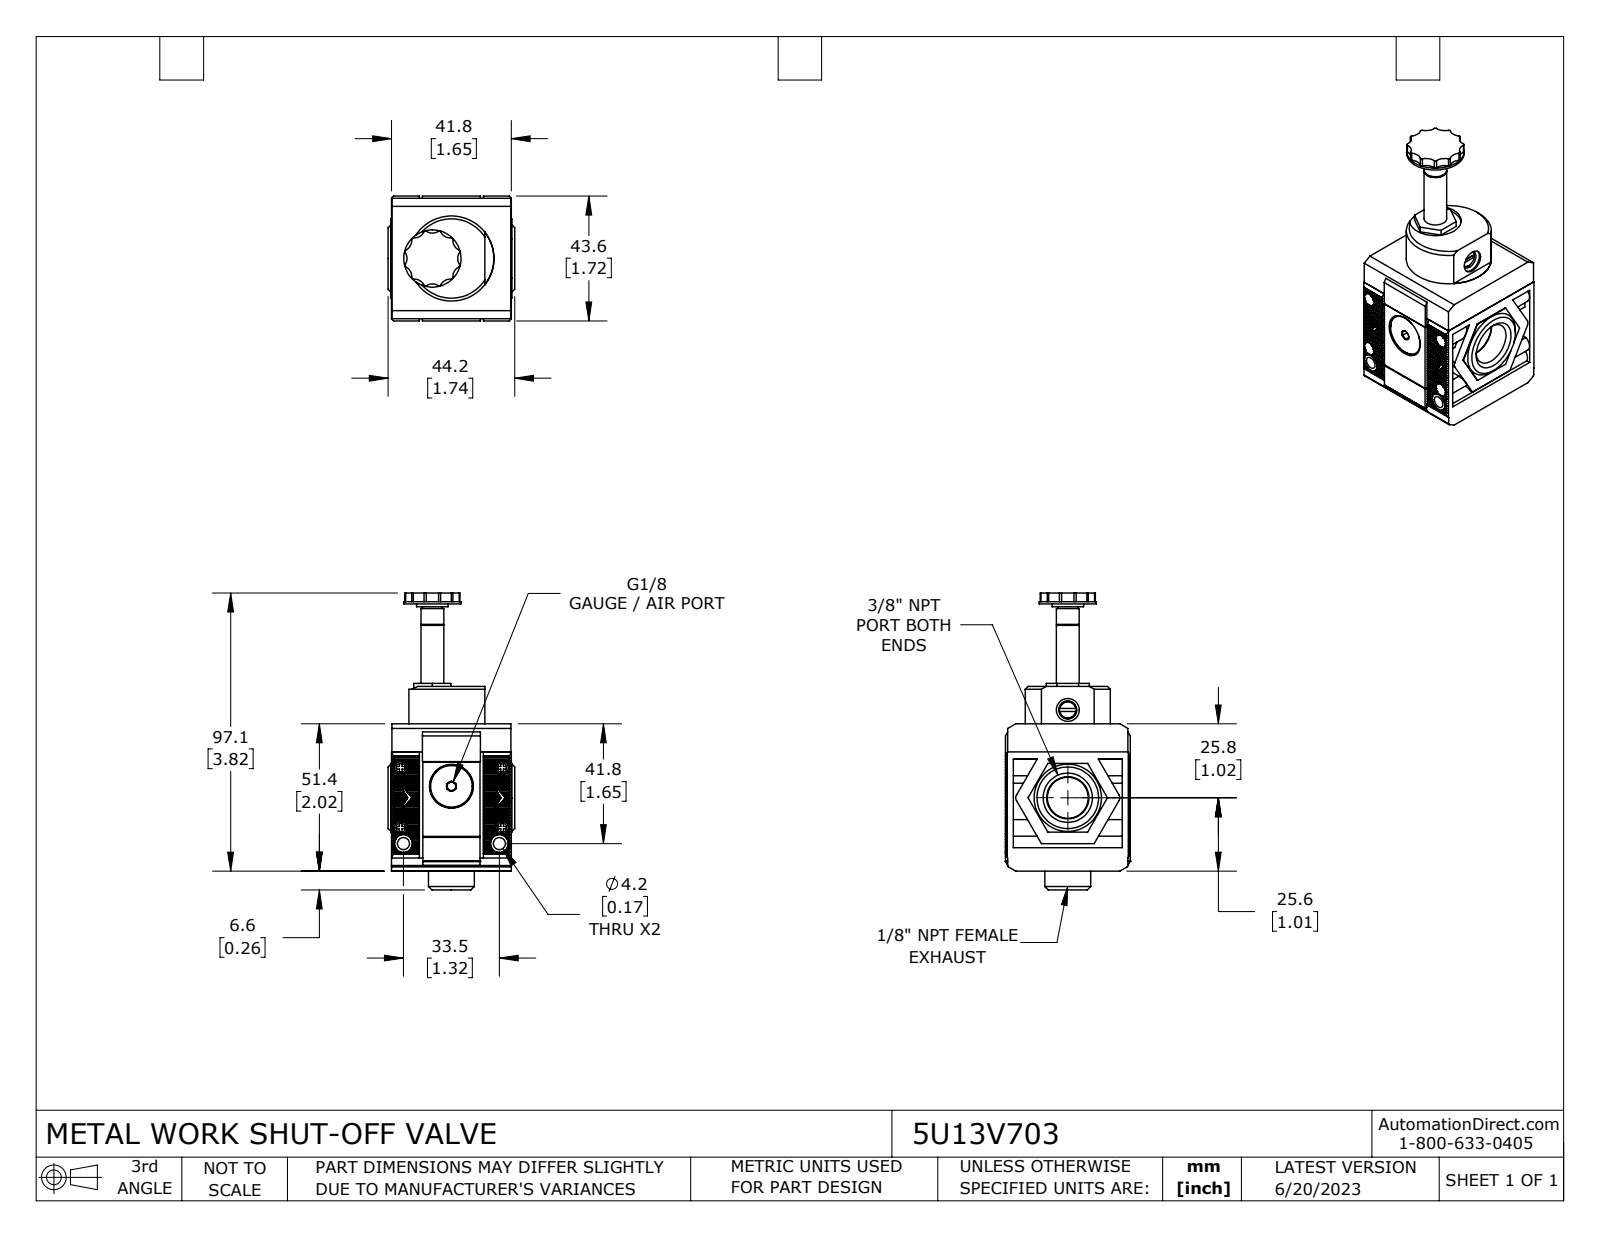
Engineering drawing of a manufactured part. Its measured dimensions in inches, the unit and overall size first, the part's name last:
Units: inches
Overall size (bounding box): 4.081 × 1.74 × 1.717
Round holes (diameter × count): ⌀0.083 ×4, ⌀0.118 ×4, ⌀0.185 ×4, ⌀0.165 ×2, ⌀0.337 ×2, ⌀0.248 ×1, ⌀0.315 ×1, ⌀0.602 ×1, ⌀1.169 ×1, ⌀1.232 ×1
Round bosses / shafts (diameter × count): ⌀0.181 ×4, ⌀0.102 ×4, ⌀0.244 ×2, ⌀1.26 ×1, ⌀0.898 ×1, ⌀0.787 ×1, ⌀0.717 ×1, ⌀0.63 ×1
Partial cylindrical surfaces — rounded edges, fillets, slot ends (radius × count): R0.02 ×12, R0.148 ×12, R0.024 ×4, R0.122 ×4, R0.008 ×2, R0.079 ×2, R0.354 ×1
Main face-to-face distances: 1.638, 1.642, 1.339, 1.673, 0.307, 0.11, 0.043, 0.386, 0.031, 1.646
Hole centre spacings: 0.222, 0.742, 0.823, 0.9, 1.027, 1.042, 1.374, 1.394
Volume: 5.989 in³ · Surface area: 54.61 in²
Bodies: 13 solids, 1178 faces (809 planar, 236 cylindrical, 133 other)
Part name (STEP PRODUCT): 5U13V703
STEP written by: SolidWorks 2021 (CONFIG_CONTROL_DESIGN)
